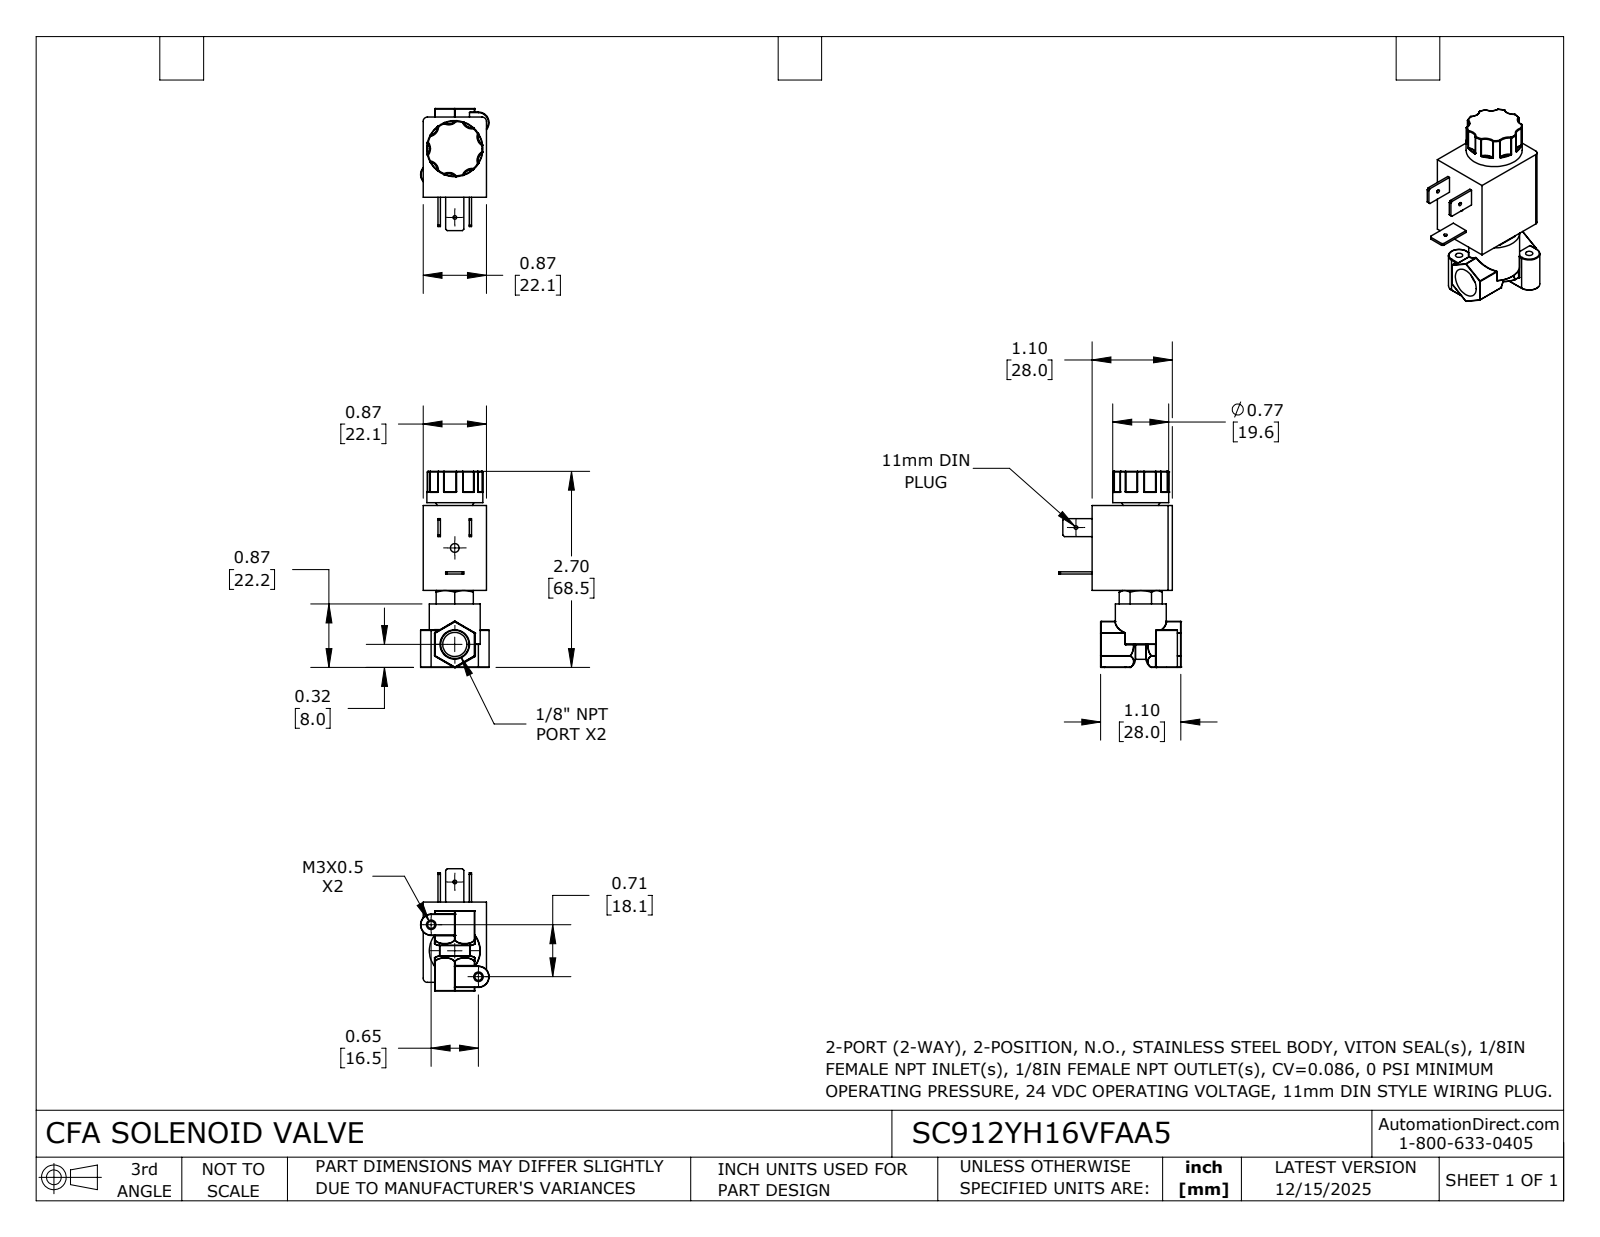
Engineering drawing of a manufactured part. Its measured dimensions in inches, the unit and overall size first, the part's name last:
Units: inches
Overall size (bounding box): 2.695 × 1.678 × 0.942
Round holes (diameter × count): ⌀0.05 ×2, ⌀0.1 ×2, ⌀0.12 ×1, ⌀0.332 ×1
Round bosses / shafts (diameter × count): ⌀0.77 ×1, ⌀0.7 ×1
Partial cylindrical surfaces — rounded edges, fillets, slot ends (radius × count): R0.004 ×29, R0.01 ×18, R0.008 ×12, R0.133 ×7, R0.017 ×2, R0.06 ×2, R0.132 ×2, R0.146 ×2
Main face-to-face distances: 0.87, 1.104, 1.167, 1.637, 0.47, 0.548, 0.031, 0.161, 0.709, 1.207
Hole centre spacings: 0.672, 0.965, 1.326, 1.342
Volume: 1.739 in³ · Surface area: 14.05 in²
Bodies: 1 solid, 397 faces (76 planar, 110 cylindrical, 211 other)
Part name (STEP PRODUCT): SC912YH16VFAA5
STEP written by: SolidWorks 2024 (CONFIG_CONTROL_DESIGN)
